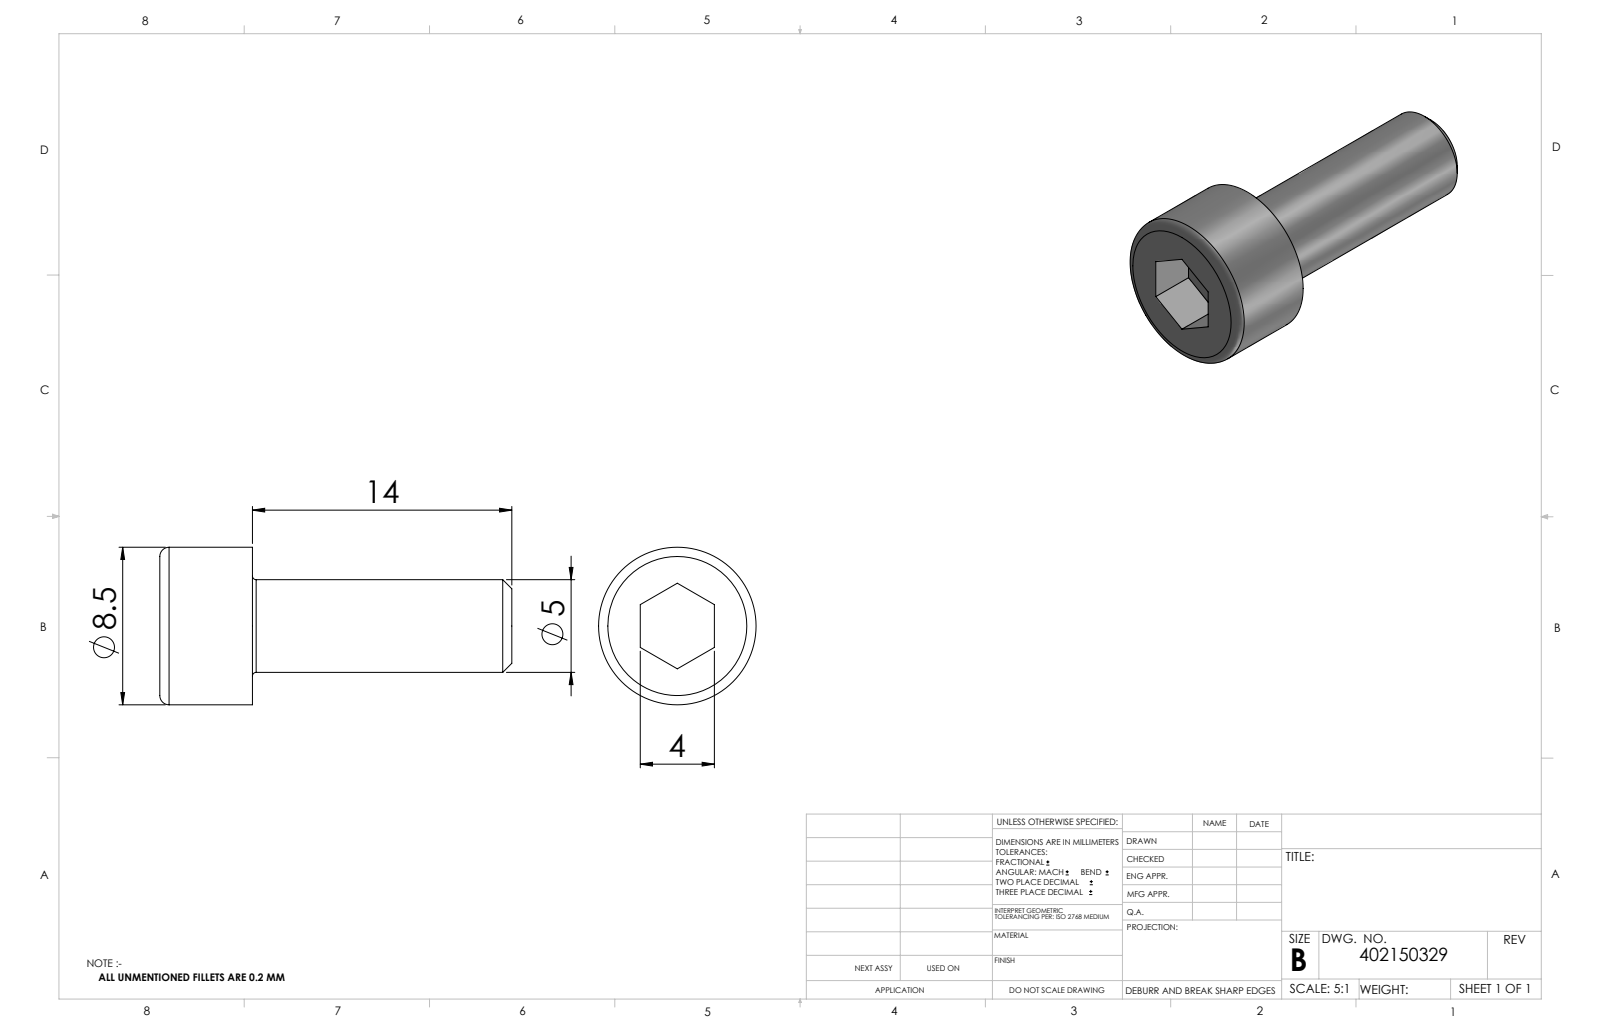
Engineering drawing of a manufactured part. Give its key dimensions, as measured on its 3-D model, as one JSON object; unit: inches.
{"part_name": "402150329_c_1", "step_written_by": "SolidWorks 2014 (CONFIG_CONTROL_DESIGN)", "units": "inches", "bodies": {"solids": 1, "faces": 20, "planar": 10, "cylindrical": 4, "other": 6}, "overall_size": [0.748, 0.335, 0.335], "volume_in3": 0.032, "surface_area_in2": 0.76, "round_bosses_or_shafts": [[0.335, 1], [0.197, 1]], "face_to_face_distances": [0.197, 0.098, 0.157, 0.748, 0.65, 0.551]}
